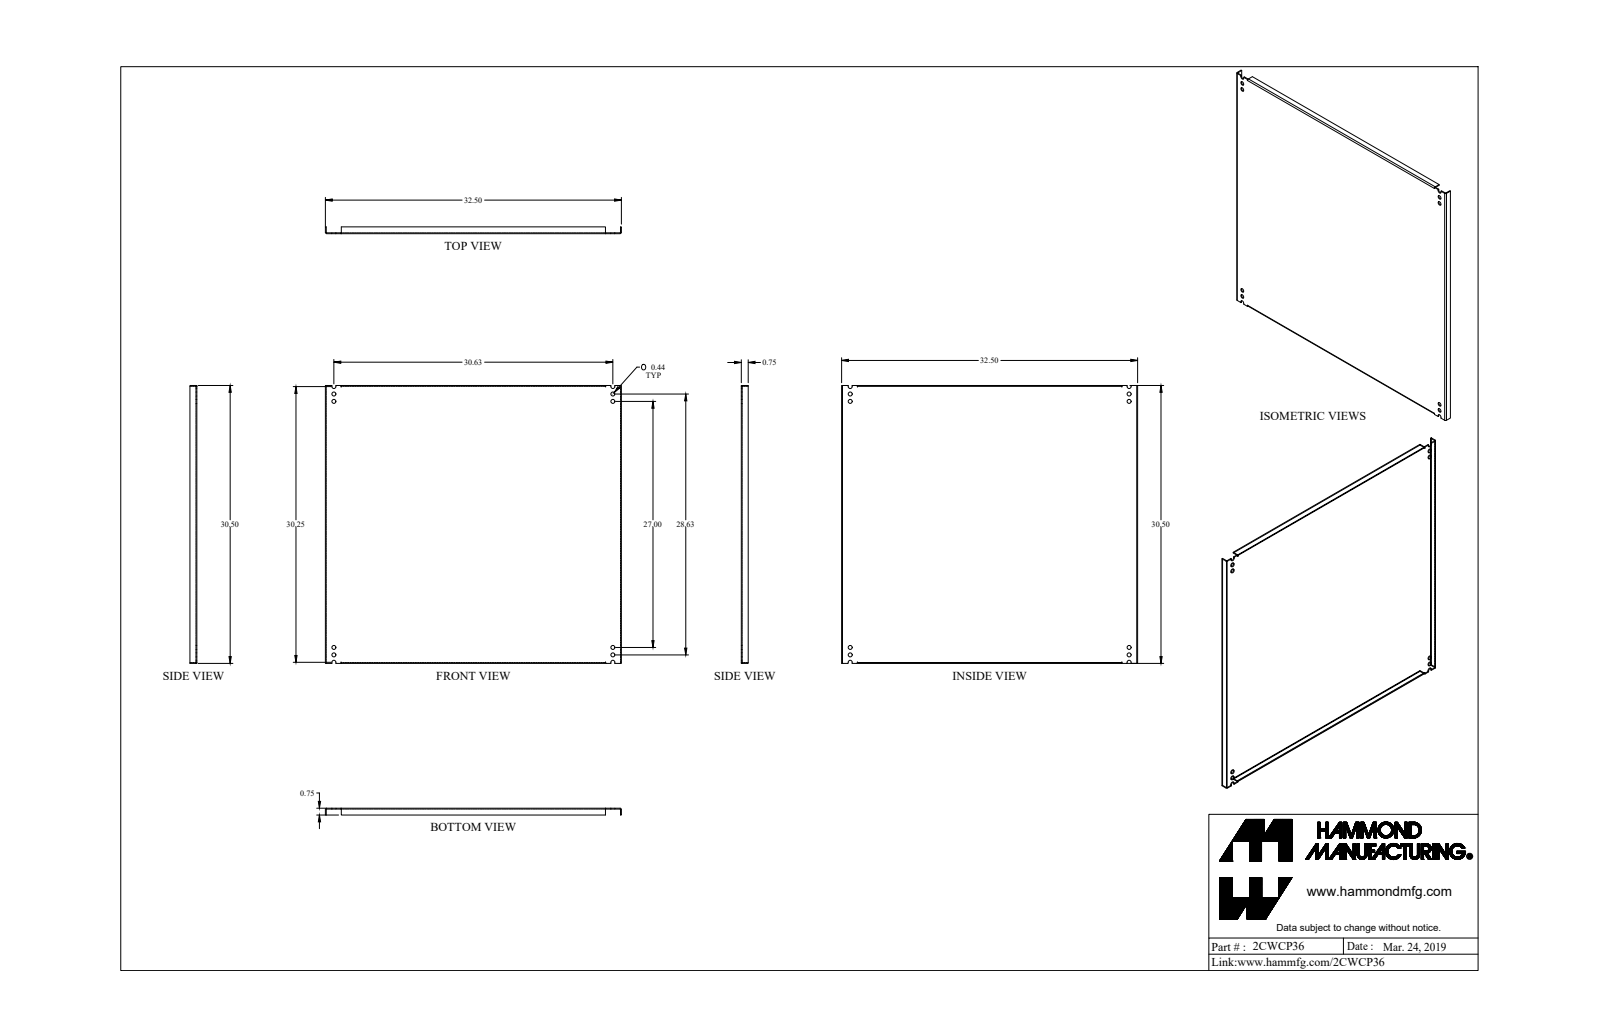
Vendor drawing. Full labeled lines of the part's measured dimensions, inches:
Part name (STEP PRODUCT): 2CWCP36
STEP written by: SolidWorks 2018 (AUTOMOTIVE_DESIGN)
Units: inches
Bodies: 3 solids, 75 faces (52 planar, 23 cylindrical, 0 other)
Overall size (bounding box): 32.5 × 30.497 × 1.07
Volume: 101.1 in³ · Surface area: 2 142 in²
Round holes (diameter × count): ⌀0.437 ×8, ⌀0.307 ×1, ⌀0.445 ×1
Round bosses / shafts (diameter × count): ⌀1 ×1
Partial cylindrical surfaces — rounded edges, fillets, slot ends (radius × count): R0.048 ×4, R0.143 ×4, R0.219 ×4
Main face-to-face distances: 0.095, 32.405, 30.402, 32.5, 32.31, 30.497, 30.307, 0.75, 0.655, 0.096
Hole centre spacings: 30.626, 30.637, 41.37, 0.812, 0.813, 20.414, 20.415, 20.96
